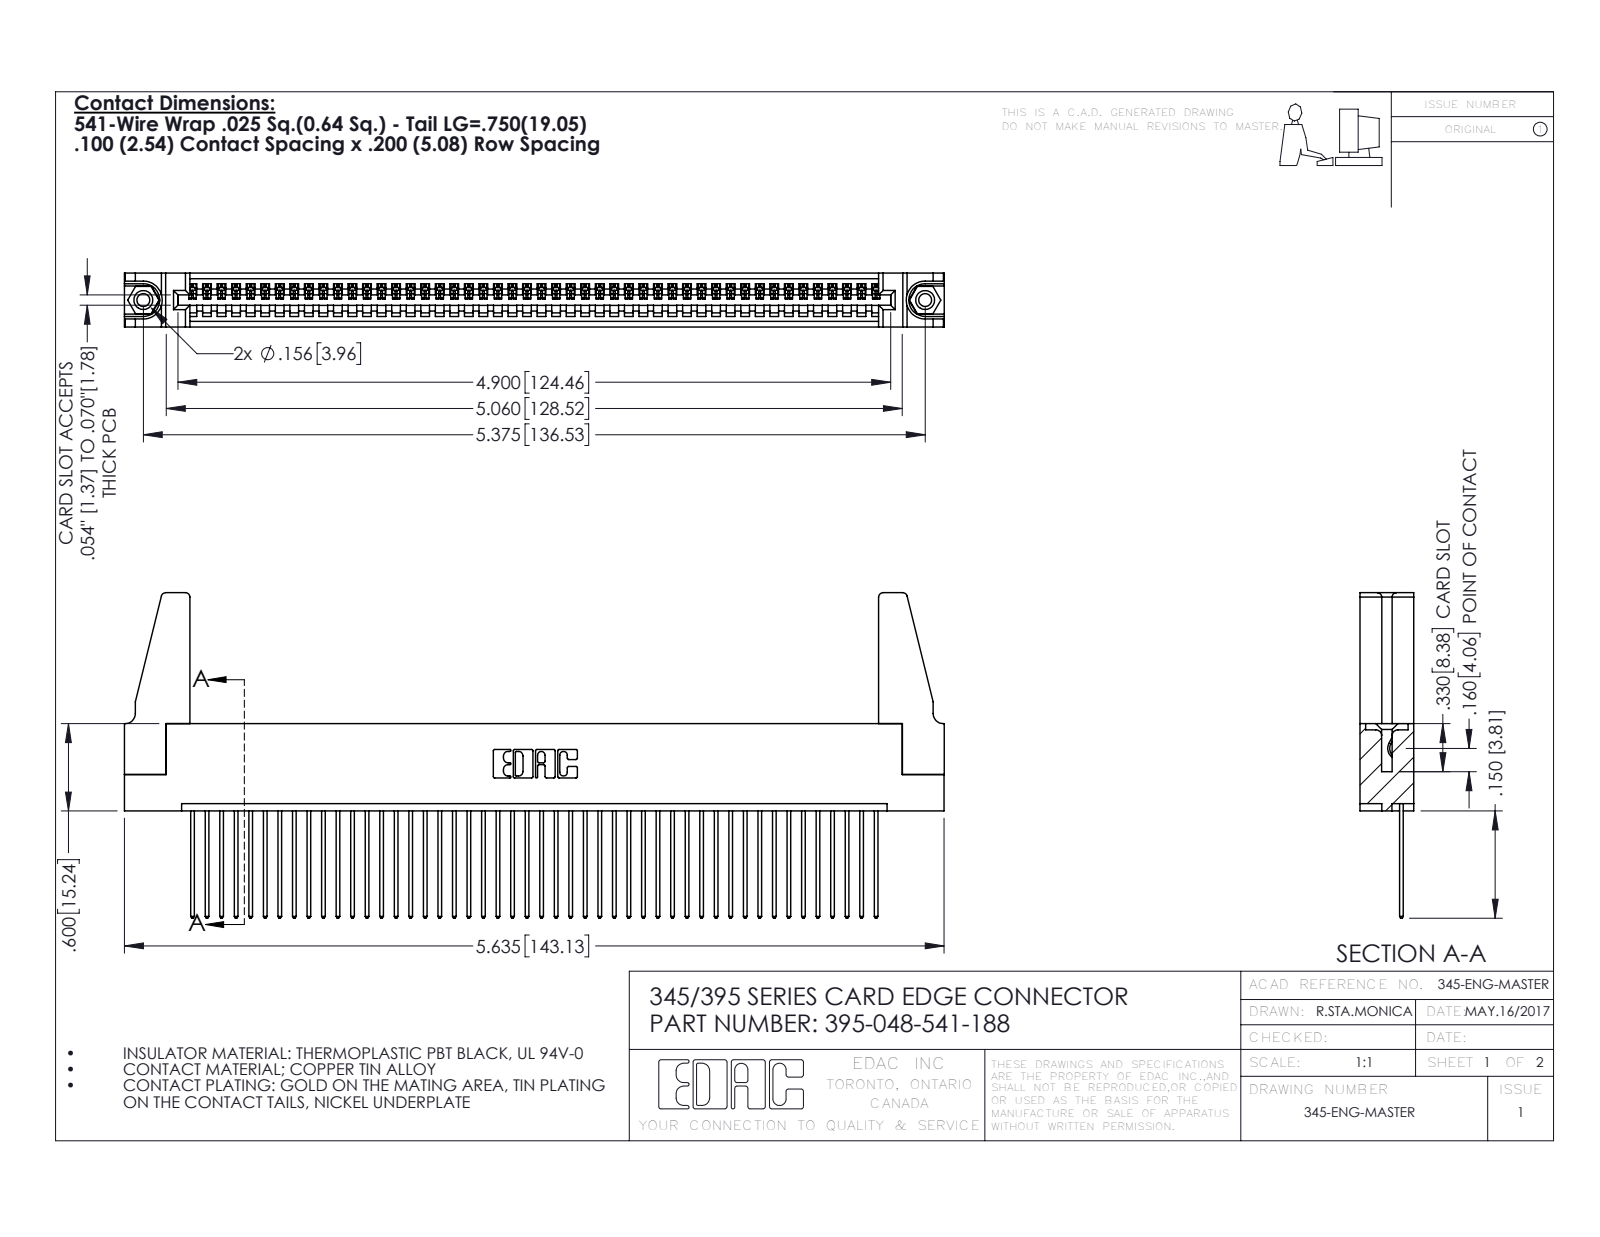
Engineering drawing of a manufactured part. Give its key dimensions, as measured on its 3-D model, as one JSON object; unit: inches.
{"part_name": "395-048-541-188; 345-220-078_345-220-088; 345-292-001_345-293-141; 345-250-001_345-250-001-102 (+1 more)", "step_written_by": "SolidWorks 2016 (CONFIG_CONTROL_DESIGN)", "units": "inches", "bodies": {"solids": 53, "faces": 3034, "planar": 2072, "cylindrical": 946, "other": 16}, "overall_size": [5.636, 2.237, 0.37], "volume_in3": 1.041, "surface_area_in2": 34.86, "round_holes": [[0.089, 2], [0.125, 2], [0.156, 2], [0.064, 1]], "round_bosses_or_shafts": [[0.155, 2]], "partial_cylinders_radius": [[0.006, 96], [0.01, 96], [0.01, 22], [0.03, 8], [0.007, 6], [0.031, 6], [0.026, 3], [0.031, 2]], "face_to_face_distances": [0.072, 0.298, 0.37, 0.098, 0.272, 0.025, 0.2, 0.225, 0.149, 0.072], "hole_center_spacings": [0.27, 5.139, 5.375]}
